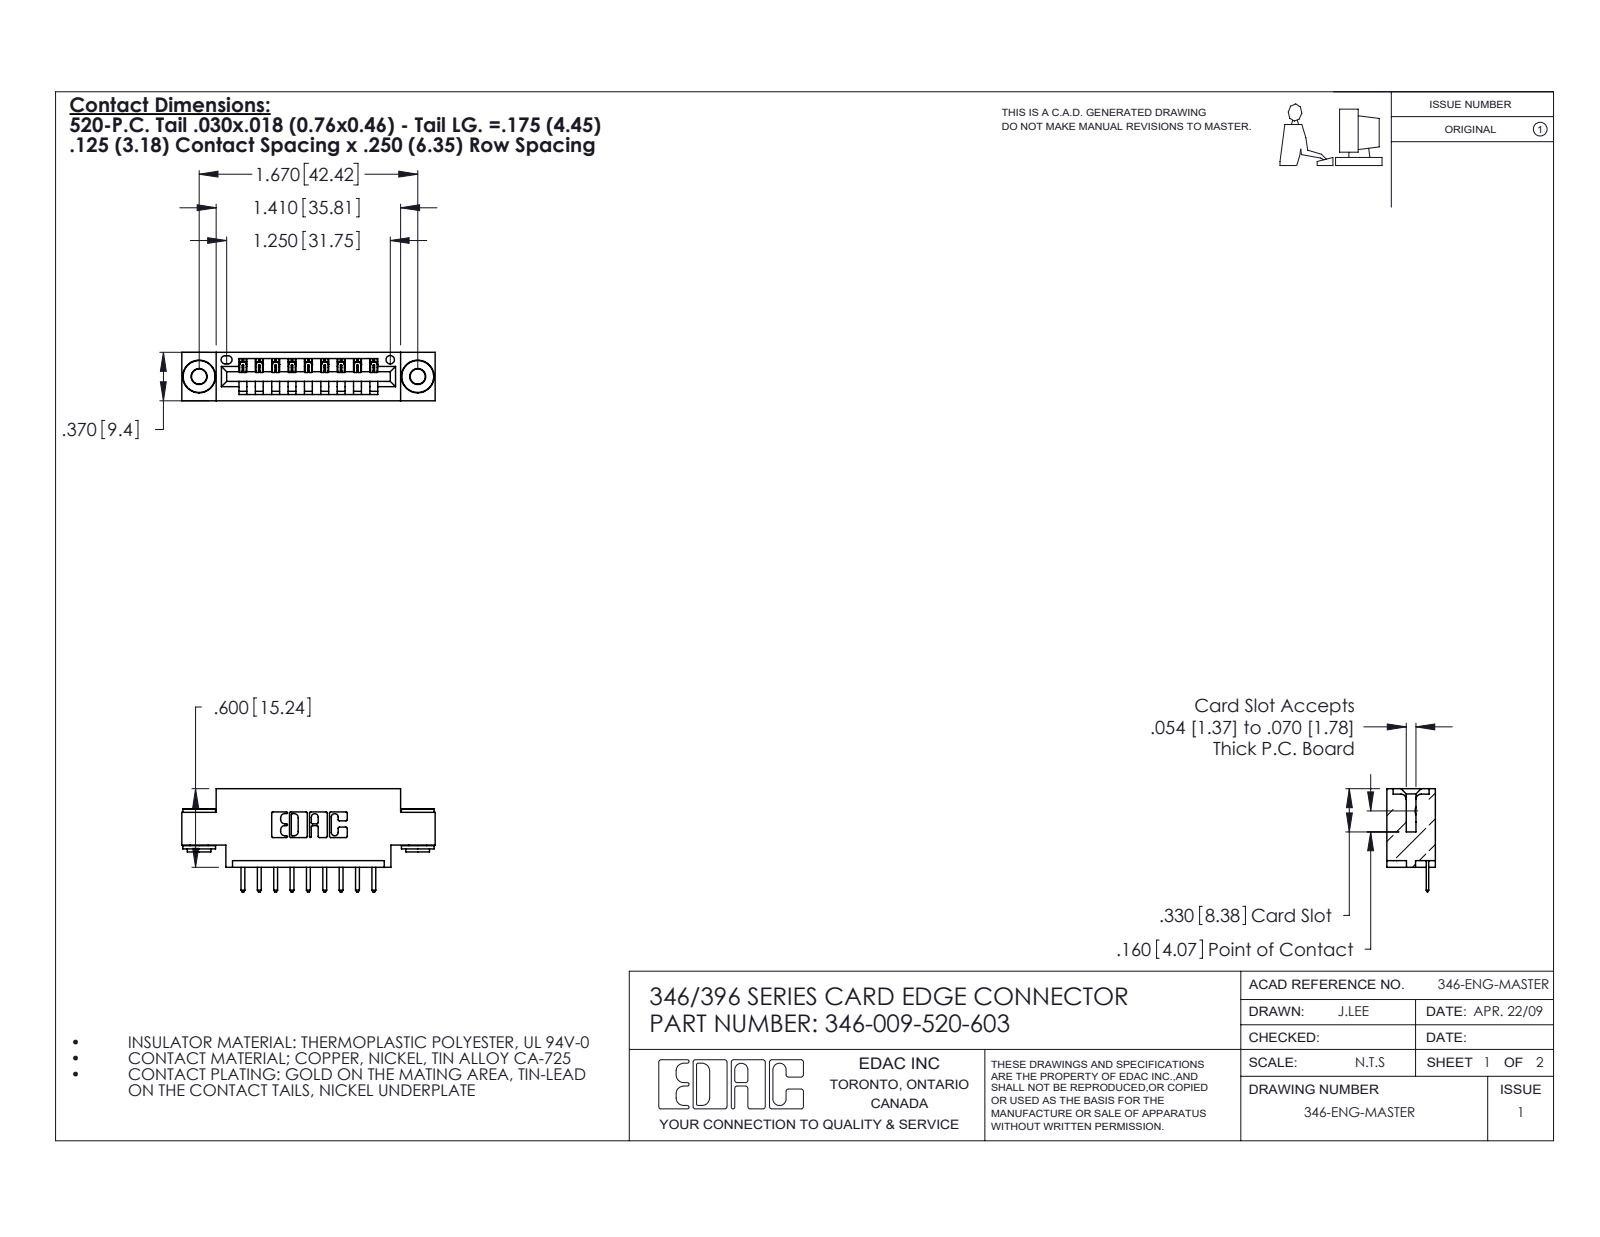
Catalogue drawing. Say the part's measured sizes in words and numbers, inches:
The part is named "345-250-002_345-250-002-102; 346-009-520-603; 346 Part_0.170 Offset - 0.156 Dia-TH; 345-292-001_345-293-120". Its 3-D file was written by "SolidWorks 2020 (CONFIG_CONTROL_DESIGN)". It is 12 solids with 736 faces: 482 planar, 246 cylindrical and 8 other. Overall it measures 1.935 by 0.788 by 0.37 inches. Its volume is 0.262 cubic inches and its surface area 8.279 square inches. Round holes: 2 of diameter 0.116, 2 of diameter 0.156, 1 of diameter 0.064. Round bosses or shafts: 2 of diameter 0.25, 2 of diameter 0.18, 2 of diameter 0.136. Partial cylindrical surfaces (rounded edges, fillets, slot ends): 22 of radius 0.01, 20 of radius 0.01, 18 of radius 0.006, 6 of radius 0.007, 6 of radius 0.031, 3 of radius 0.026, 2 of radius 0.031, 2 of radius 0.04. The main face-to-face distances are 0.25, 0.37, 0.048, 0.322, 0.025, 0.222, 0.148, 0.1, 0.174, 0.275. The hole center spacings are 0.246, 1.465, 1.67.
